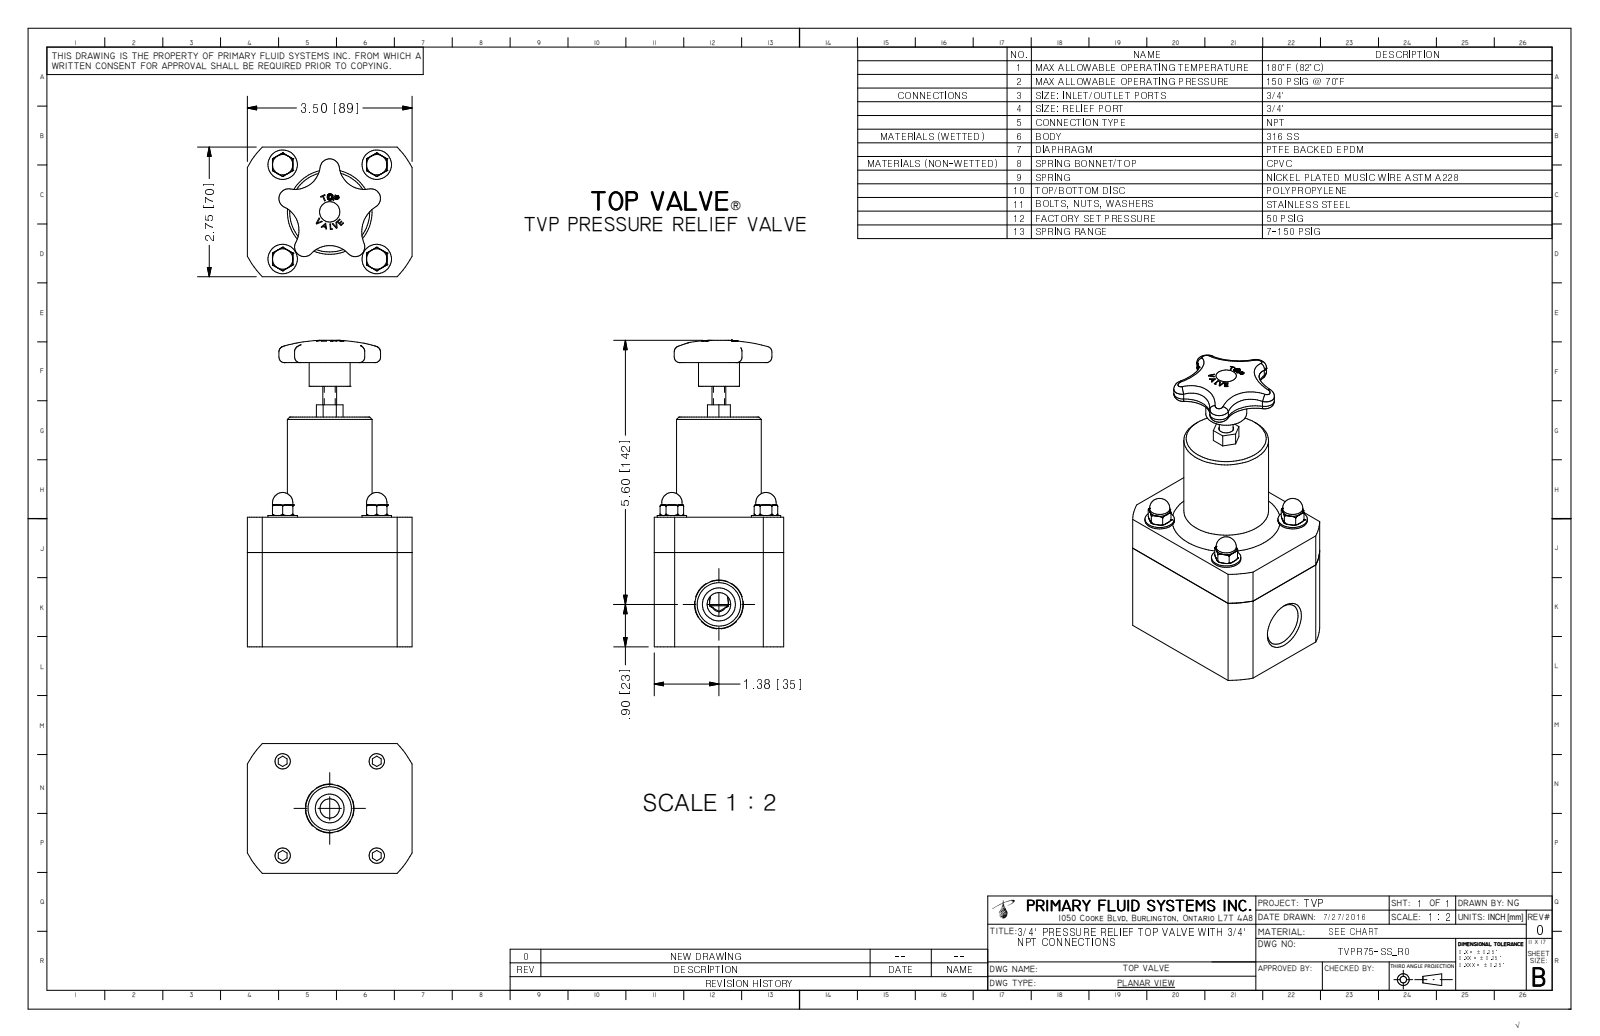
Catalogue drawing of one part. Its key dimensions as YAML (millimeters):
part_name: "TVPR75-SS_R0"
step_written_by: "Autodesk Inventor 2009 (AUTOMOTIVE_DESIGN)"
units: millimeters
bodies: {solids: 1, faces: 316, planar: 123, cylindrical: 44, other: 149}
overall_size: [165.1, 88.9, 69.9]
volume: 513700
surface_area: 53640
round_holes:
  - {diameter: 4.4, count: 4}
  - {diameter: 23.4, count: 2}
  - {diameter: 61, count: 1}
round_bosses_or_shafts:
  - {diameter: 15.9, count: 4}
  - {diameter: 11, count: 4}
  - {diameter: 60.3, count: 1}
  - {diameter: 45.7, count: 1}
  - {diameter: 22.1, count: 1}
  - {diameter: 7.4, count: 1}
partial_cylinders:
  - {radius: 2.2, count: 5}
  - {radius: 5.2, count: 5}
  - {radius: 13.6, count: 4}
  - {radius: 16.7, count: 4}
  - {radius: 15.9, count: 1}
  - {radius: 18.9, count: 1}
  - {radius: 50.5, count: 1}
face_to_face_distances: [69.9, 69.9, 88.9, 123.8, 54, 19.1, 50.8, 15.2, 54.6, 108.6]
hole_center_spacings: [35.9, 50.8, 71.8]
